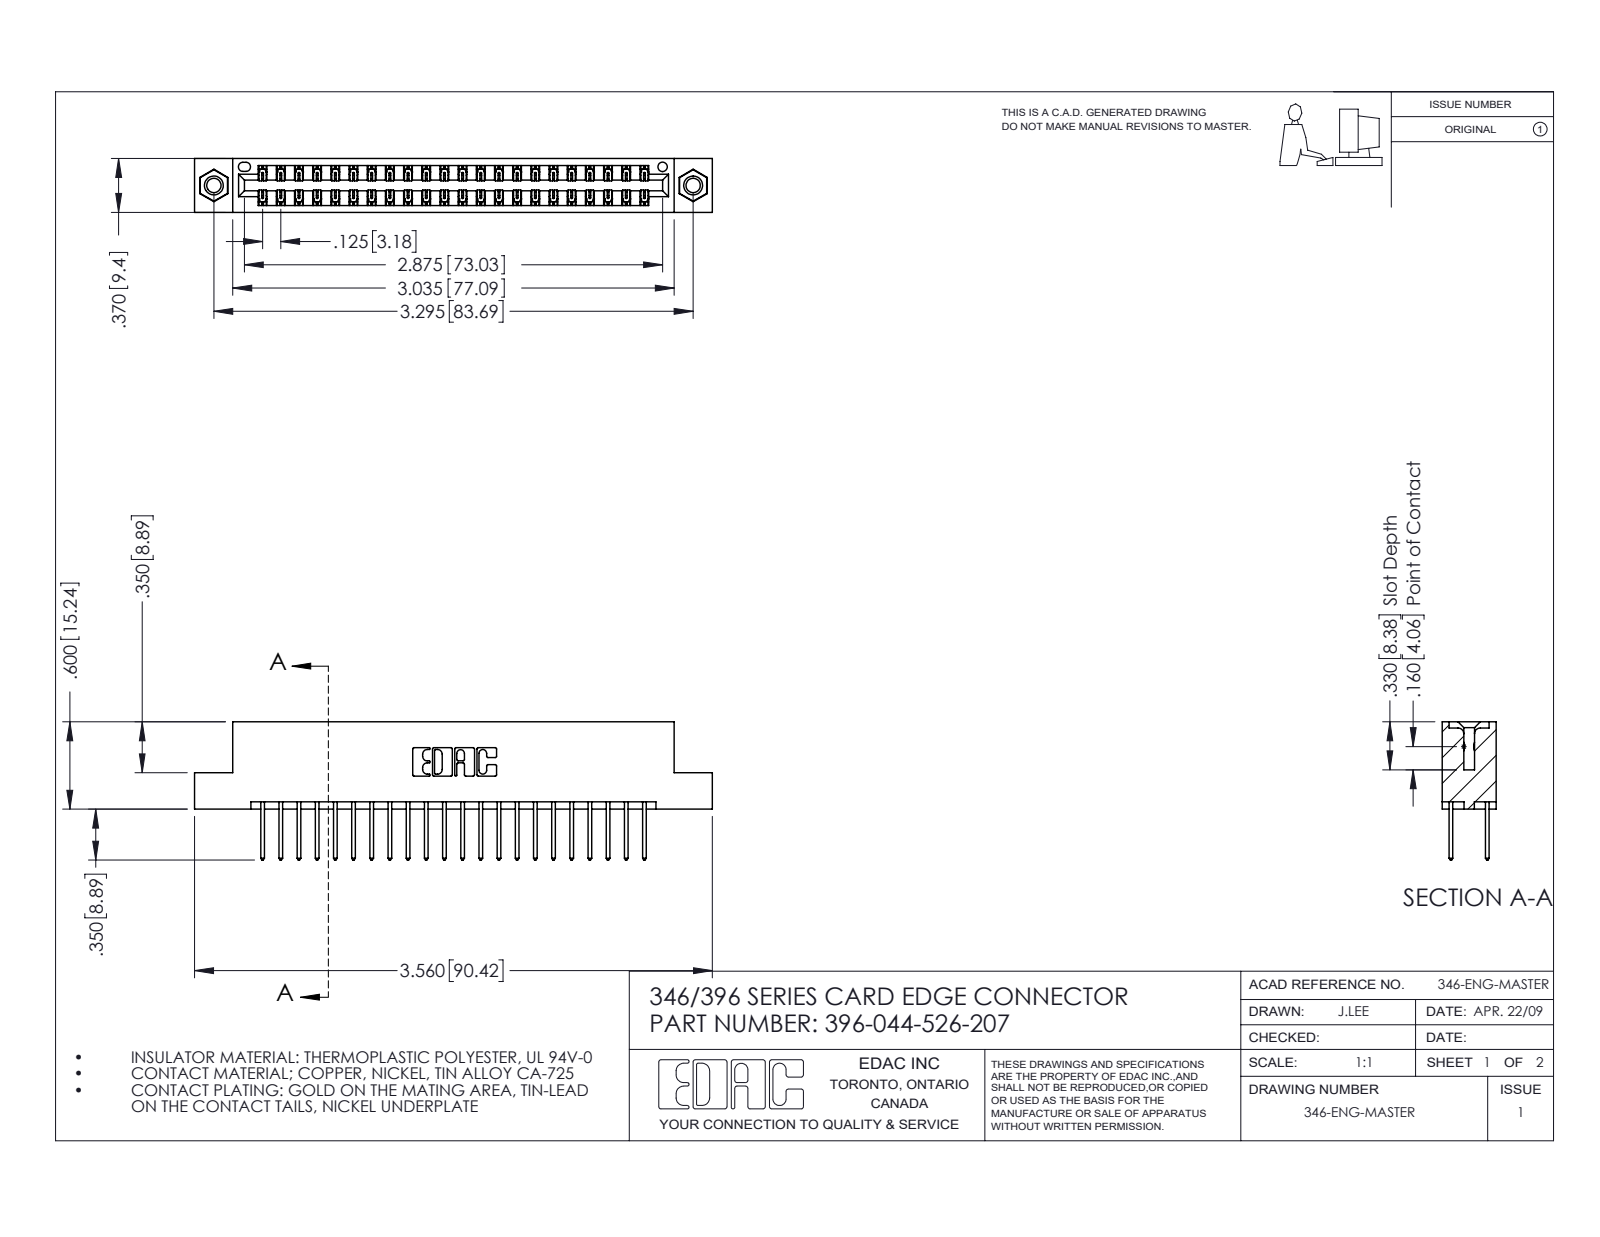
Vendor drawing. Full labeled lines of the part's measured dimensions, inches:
Part name (STEP PRODUCT): 345-292-001_345-293-126; 346 Part_Flush Mounting Lugs - 0.156 Dia-TI; 345-250-001_345-250-005-103; 396-044-526-207
STEP written by: SolidWorks 2016 (CONFIG_CONTROL_DESIGN)
Units: inches
Bodies: 47 solids, 2470 faces (1648 planar, 806 cylindrical, 16 other)
Overall size (bounding box): 3.56 × 0.95 × 0.37
Volume: 0.532 in³ · Surface area: 18.65 in²
Round holes (diameter × count): ⌀0.098 ×2, ⌀0.125 ×2, ⌀0.156 ×2, ⌀0.064 ×1
Round bosses / shafts (diameter × count): ⌀0.155 ×2
Partial cylindrical surfaces — rounded edges, fillets, slot ends (radius × count): R0.006 ×66, R0.01 ×44, R0.01 ×22, R0.007 ×6, R0.031 ×6, R0.026 ×3, R0.014 ×2, R0.022 ×2
Main face-to-face distances: 0.048, 0.322, 0.25, 0.37, 0.072, 0.298, 0.025, 0.275, 0.148, 0.222
Hole centre spacings: 0.246, 3.087, 3.295
